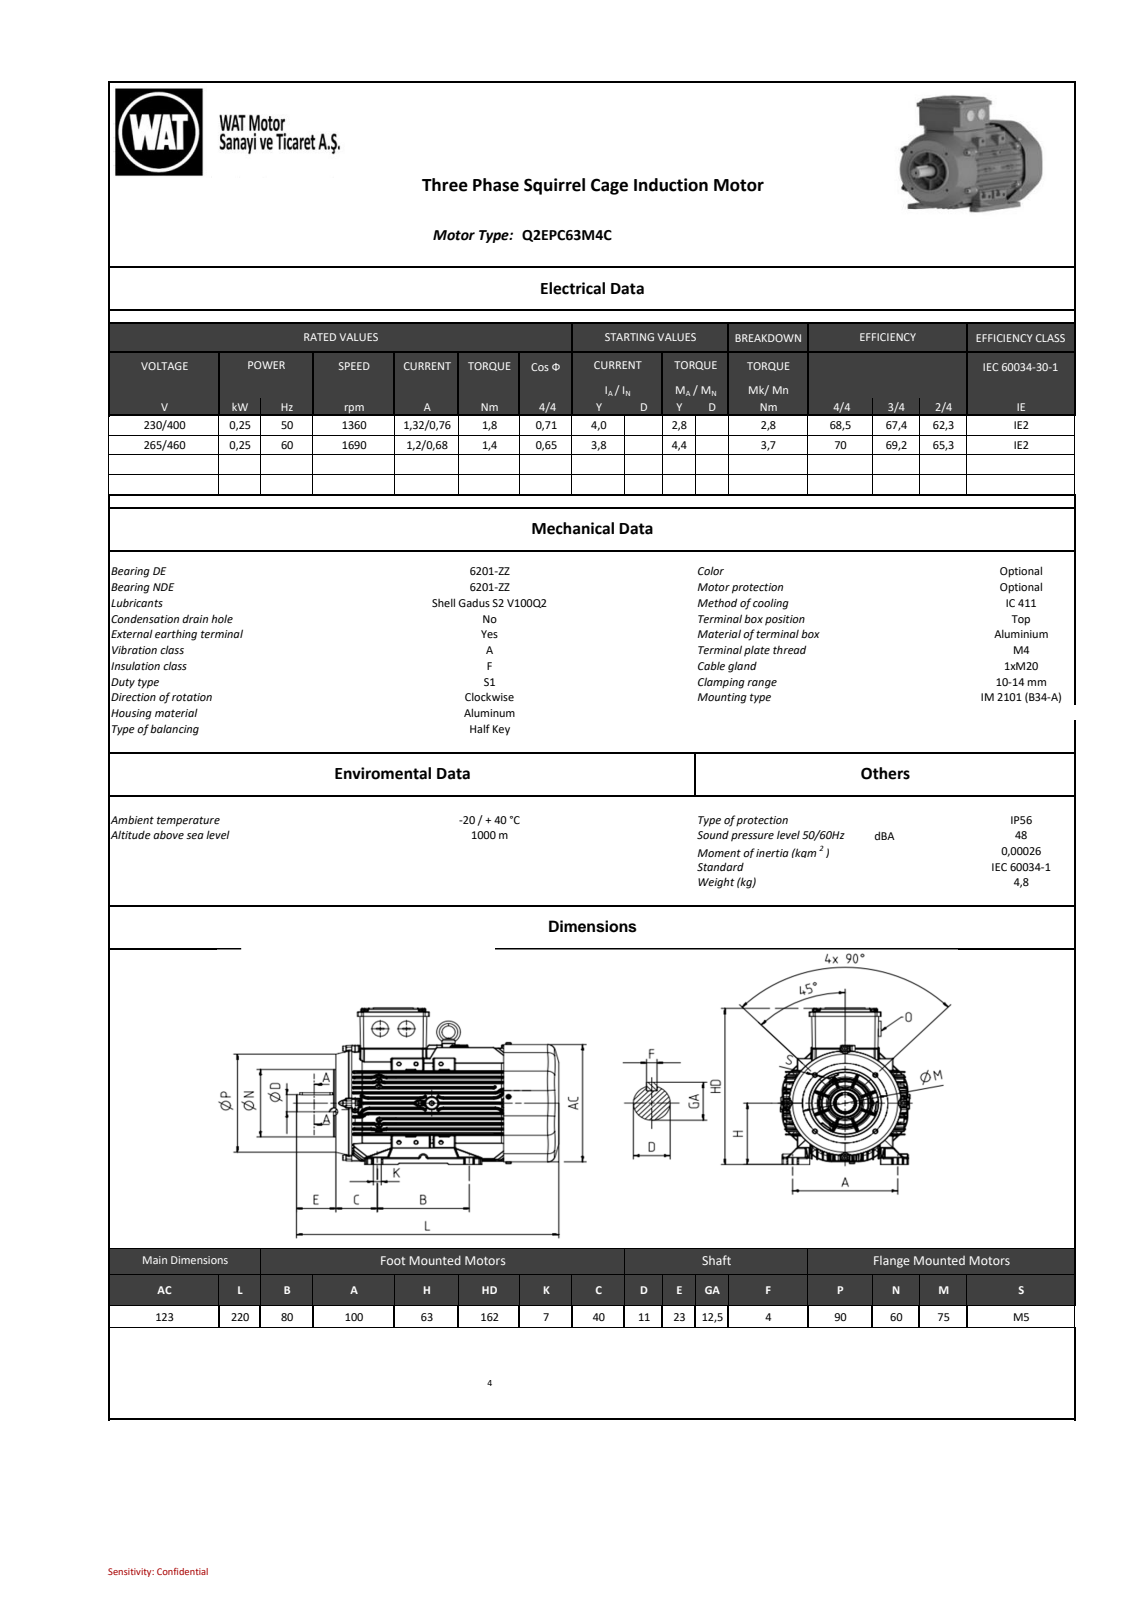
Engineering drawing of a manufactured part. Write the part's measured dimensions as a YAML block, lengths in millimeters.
part_name: "QE series_ 63_B34a_stp_objects"
step_written_by: "SIEMENS PLM Software NX2206.8101 (AP203_CONFIGURATION_CONTROLLED_3D_DESIGN_OF_MECHANICAL_PARTS_AND_ASSEMBLIES_MIM_LF)"
units: millimeters
bodies: {solids: 0, faces: 1583, planar: 822, cylindrical: 505, other: 256}
overall_size: [219.46, 161.1, 128]
round_holes:
  - {diameter: 2.5, count: 4}
  - {diameter: 3.65, count: 4}
  - {diameter: 3.8, count: 4}
  - {diameter: 4.2, count: 4}
  - {diameter: 5, count: 4}
  - {diameter: 3, count: 2}
  - {diameter: 7, count: 2}
  - {diameter: 8, count: 1}
  - {diameter: 11.2, count: 1}
  - {diameter: 14.5, count: 1}
round_bosses_or_shafts:
  - {diameter: 8, count: 8}
  - {diameter: 4, count: 4}
  - {diameter: 123, count: 1}
  - {diameter: 121, count: 1}
  - {diameter: 60, count: 1}
  - {diameter: 26, count: 1}
  - {diameter: 19, count: 1}
partial_cylinders:
  - {radius: 0.5, count: 108}
  - {radius: 1, count: 84}
  - {radius: 1.5, count: 28}
  - {radius: 0.1, count: 14}
  - {radius: 1.35, count: 12}
  - {radius: 4, count: 12}
  - {radius: 2, count: 8}
  - {radius: 2.5, count: 7}
face_to_face_distances: [27.96, 13.97, 14.16, 6.93, 2, 6.88, 21.03, 7.01, 20.9, 7.06]
hole_center_spacings: [37.5, 54, 63, 82.98, 10, 5, 16.93, 20.38]
